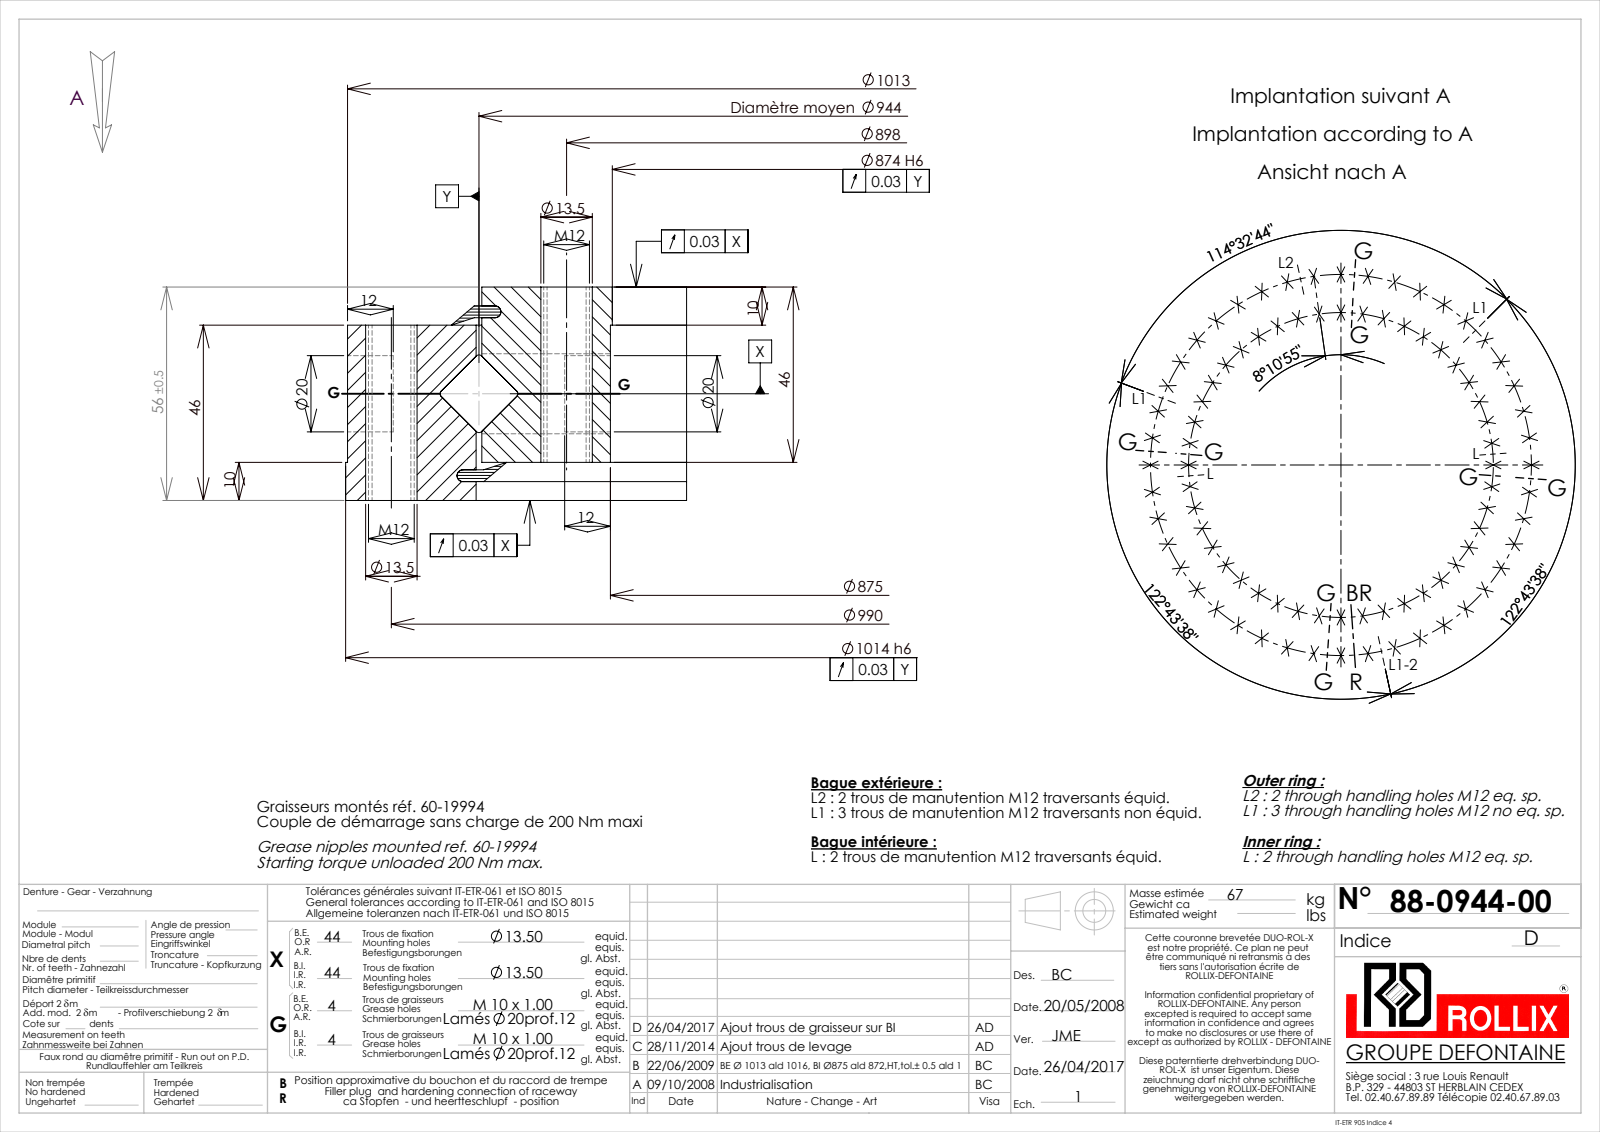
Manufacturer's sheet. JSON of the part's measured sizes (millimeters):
{"part_name": "88-0944-00", "step_written_by": "SolidWorks 2016 (CONFIG_CONTROL_DESIGN)", "units": "millimeters", "bodies": {"solids": 13, "faces": 495, "planar": 104, "cylindrical": 262, "other": 129}, "overall_size": [1014, 1014, 56], "volume_mm3": 8117000, "surface_area_mm2": 1396000, "round_holes": [[13.5, 88], [9, 8], [20, 8], [12, 6], [874, 1], [875, 1], [945.5, 1], [955.5, 1]], "round_bosses_or_shafts": [[10, 8], [1014, 1], [1013, 1], [942.5, 1], [932.5, 1], [15, 1]], "face_to_face_distances": [46, 10, 36, 56, 4.95, 51.05, 5.05, 41.05, 8.05, 47.95], "hole_center_spacings": [495, 140.89, 345.97, 210.44, 70.62, 535.24, 278.91, 593.29]}
